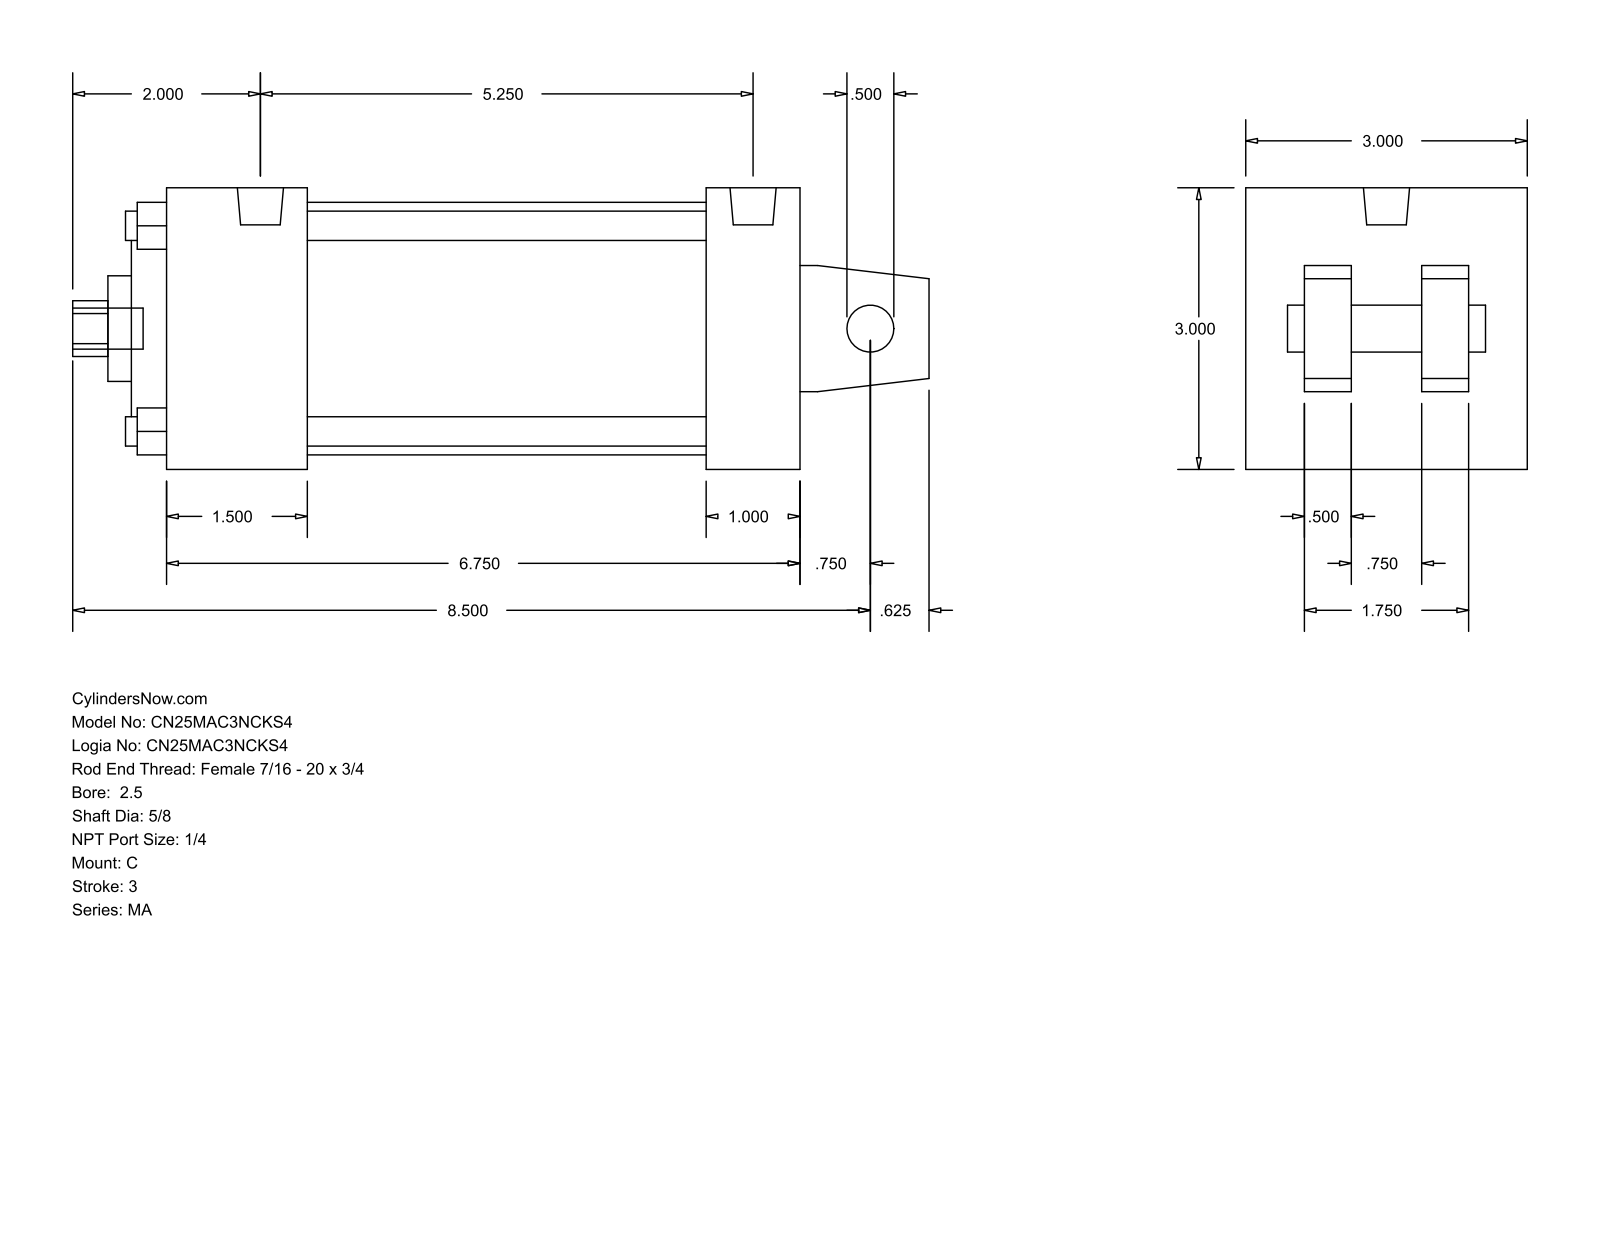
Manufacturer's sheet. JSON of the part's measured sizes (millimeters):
{"part_name": "MA_C__0250_0.625", "step_written_by": "GSSL Pune (CONFIG_CONTROL_DESIGN)", "units": "millimeters", "bodies": {"solids": 0, "faces": 105, "planar": 77, "cylindrical": 28, "other": 0}, "overall_size": [231.78, 76.2, 76.2], "round_holes": [[7.94, 4], [12.7, 1], [15.88, 1], [28.57, 1], [50.8, 1], [68.33, 1]], "round_bosses_or_shafts": [[7.94, 4], [12.49, 2], [11.11, 1]], "partial_cylinders_radius": [[7.54, 1]], "face_to_face_distances": [76.2, 171.45, 12.7, 15.87, 60.33, 47.63, 25.4, 38.1, 146.05, 107.95], "hole_center_spacings": [39.33, 55.62, 78.66]}
